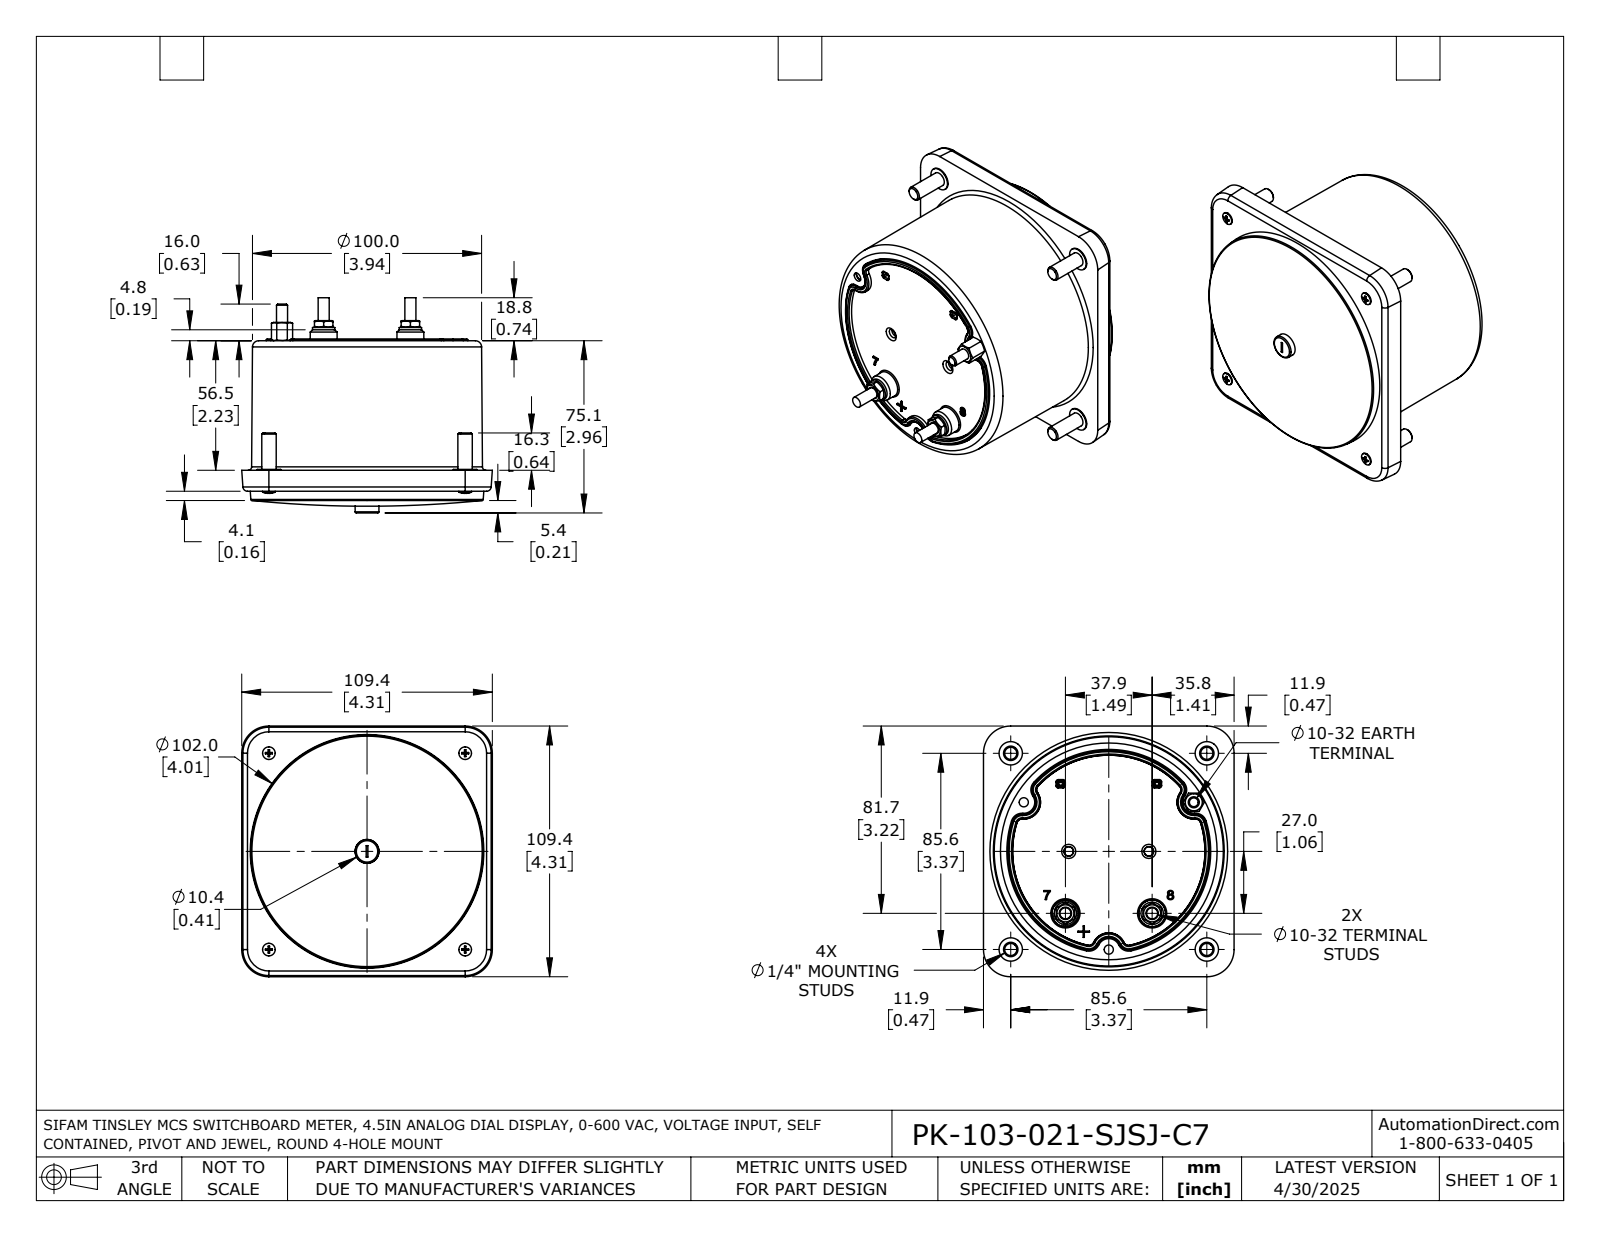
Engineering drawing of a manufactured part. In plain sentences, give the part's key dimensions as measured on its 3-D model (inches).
The part is named "PK-103-021-SJSJ-C7". Its 3-D file was written by "SolidWorks 2021 (AUTOMOTIVE_DESIGN)". It is 1 solid with 609 faces: 167 planar, 141 cylindrical and 301 other. Overall it measures 4.307 by 4.307 by 3.697 inches. Its volume is 36.28 cubic inches and its surface area 82.21 square inches. Round holes: 4 of diameter 0.094, 4 of diameter 0.138, 4 of diameter 0.315, 3 of diameter 0.157, 2 of diameter 0.209. Round bosses or shafts: 4 of diameter 0.402, 4 of diameter 0.248, 4 of diameter 0.217, 4 of diameter 0.114, 3 of diameter 0.19, 2 of diameter 0.384, 1 of diameter 0.146. Partial cylindrical surfaces (rounded edges, fillets, slot ends): 24 of radius 0.02, 9 of radius 0.189, 4 of radius 0.079, 1 of radius 1.752. The main face-to-face distances are 2.177, 2.537, 0.36, 0.048, 2.225, 2.585, 0.489, 2.715, 2.667, 0.129. The hole center spacings are 3.372, 3.37, 3.374, 3.378, 3.38, 4.769, 0.971, 1.126.
